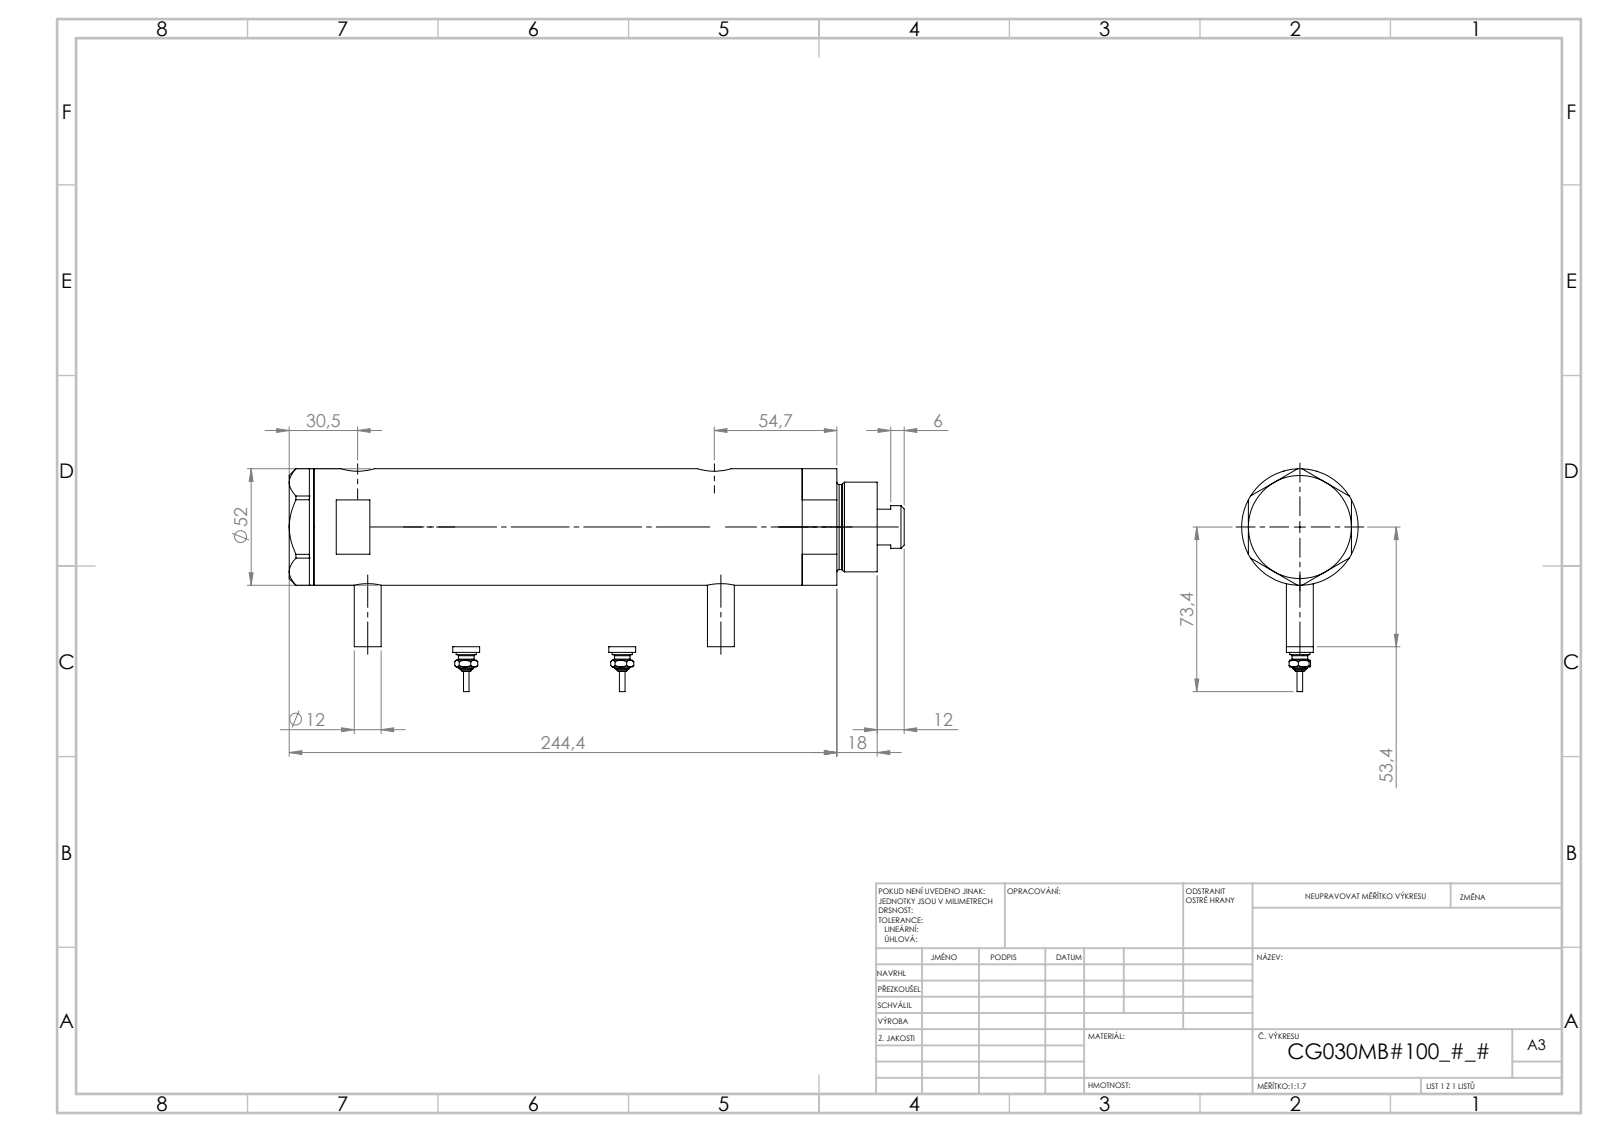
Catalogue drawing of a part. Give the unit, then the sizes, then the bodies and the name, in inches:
Units: inches
Overall size (bounding box): 10.803 × 3.913 × 2.047
Round holes (diameter × count): ⌀0.383 ×2, ⌀0.492 ×2, ⌀0.591 ×2, ⌀0.256 ×1, ⌀0.787 ×1, ⌀0.846 ×1, ⌀1.181 ×1, ⌀1.299 ×1, ⌀1.732 ×1
Round bosses / shafts (diameter × count): ⌀0.472 ×4, ⌀0.354 ×2, ⌀0.276 ×2, ⌀0.177 ×2, ⌀0.098 ×2, ⌀2.047 ×1, ⌀1.575 ×1, ⌀1.496 ×1
Main face-to-face distances: 7.146, 0.937, 6.209, 0.433, 1.37, 7.579, 1.811, 1.433, 9.012, 8.579
Hole centre spacings: 0.114, 0.177, 6.091, 6.205, 6.268, 6.382
Volume: 30.79 in³ · Surface area: 169.5 in²
Bodies: 6 solids, 226 faces (93 planar, 69 cylindrical, 64 other)
Part name (STEP PRODUCT): V270CG_FRONT; Switch; V270CG_MIDDLE; V270CG_VC (+1 more)
STEP written by: SolidWorks 2019 (CONFIG_CONTROL_DESIGN)
